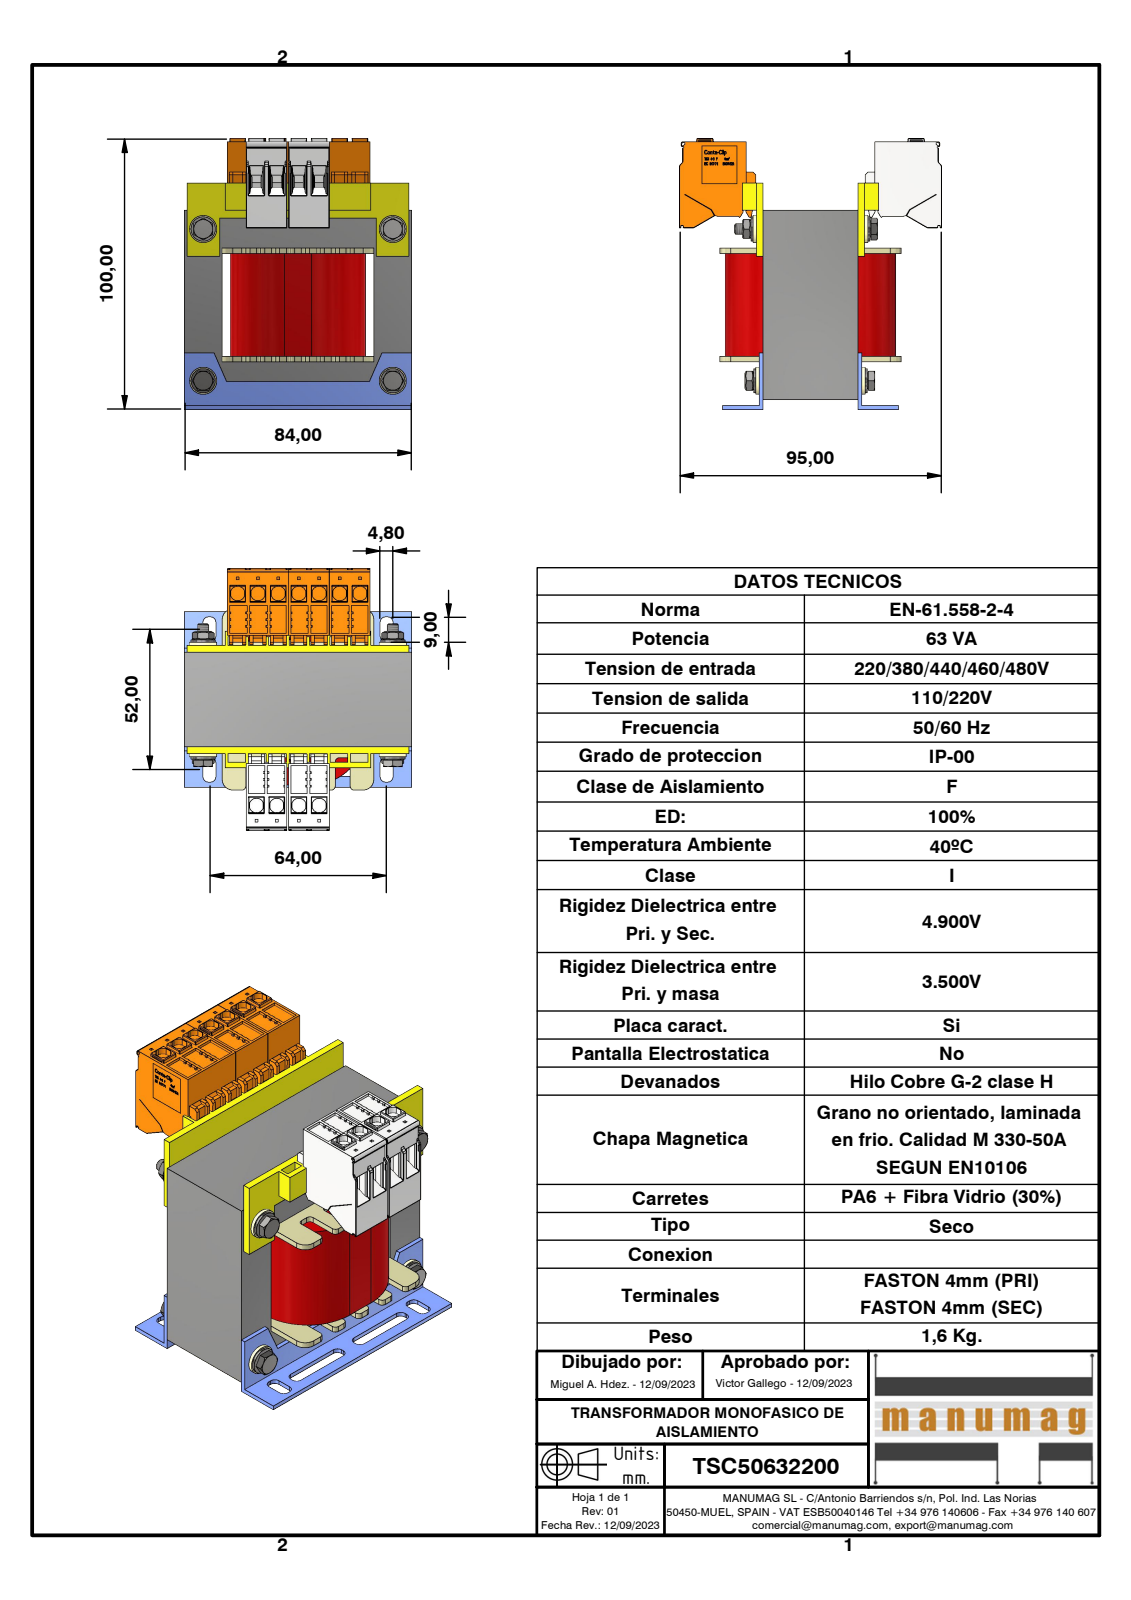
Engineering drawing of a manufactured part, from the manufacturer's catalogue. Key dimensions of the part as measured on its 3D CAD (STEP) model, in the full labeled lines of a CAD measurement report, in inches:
Part name (STEP PRODUCT): TSC50632200; EI84 x 70 - 35 (RC28); AF28DIN; EI84 (+8 more)
STEP written by: Autodesk Inventor 2023 (AUTOMOTIVE_DESIGN)
Units: inches
Bodies: 35 solids, 9166 faces (7472 planar, 1135 cylindrical, 559 other)
Overall size (bounding box): 3.945 × 3.815 × 3.307
Volume: 18.63 in³ · Surface area: 171.9 in²
Round holes (diameter × count): ⌀0.128 ×4, ⌀0.157 ×4, ⌀0.169 ×4, ⌀0.177 ×4
Round bosses / shafts (diameter × count): ⌀0.394 ×4, ⌀0.354 ×4, ⌀0.232 ×4, ⌀0.193 ×4, ⌀0.143 ×4
Partial cylindrical surfaces — rounded edges, fillets, slot ends (radius × count): R0.006 ×431, R0.008 ×122, R0.079 ×40, R0.059 ×32, R0.02 ×30, R0.012 ×12, R0.106 ×11, R0.197 ×10
Main face-to-face distances: 0.551, 2.205, 1.378, 1.102, 1.654, 2.756, 0.059, 1.535, 1.575, 0.079
Hole centre spacings: 2.205, 2.756, 3.529
